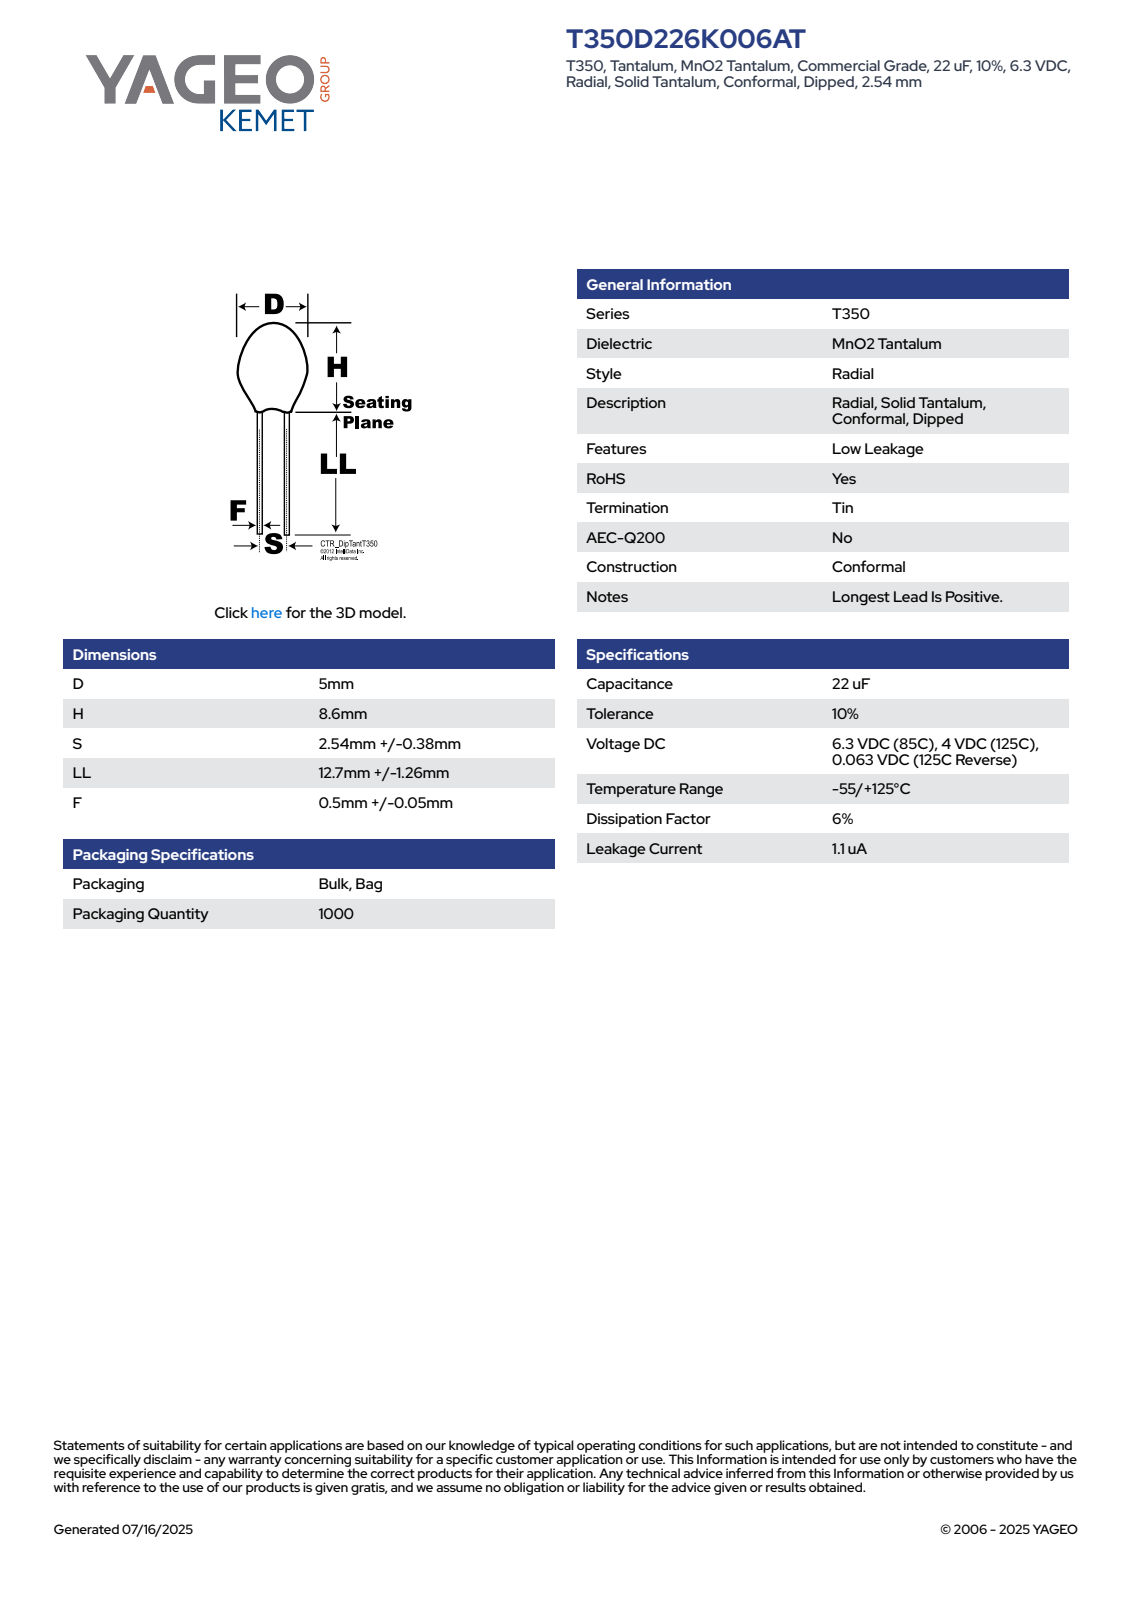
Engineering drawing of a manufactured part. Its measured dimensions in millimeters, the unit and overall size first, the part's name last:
Units: millimetres
Overall size (bounding box): 22.56 × 5 × 5
Round bosses / shafts (diameter × count): ⌀0.55 ×2, ⌀5 ×1
Partial cylindrical surfaces — rounded edges, fillets, slot ends (radius × count): R2.49 ×1
Main face-to-face distances: 8.6, 13.96, 22.56, 18.58, 4.62, 3.98, 17.78, 3.82, 0.8, 4.78
Volume: 149 mm³ · Surface area: 192 mm²
Bodies: 1 solid, 73 faces (26 planar, 10 cylindrical, 37 other)
Part name (STEP PRODUCT): CTR_T350_D5H8.6S2.54LL13.96F0.55
STEP written by: SolidWorks 2014 (AUTOMOTIVE_DESIGN)
